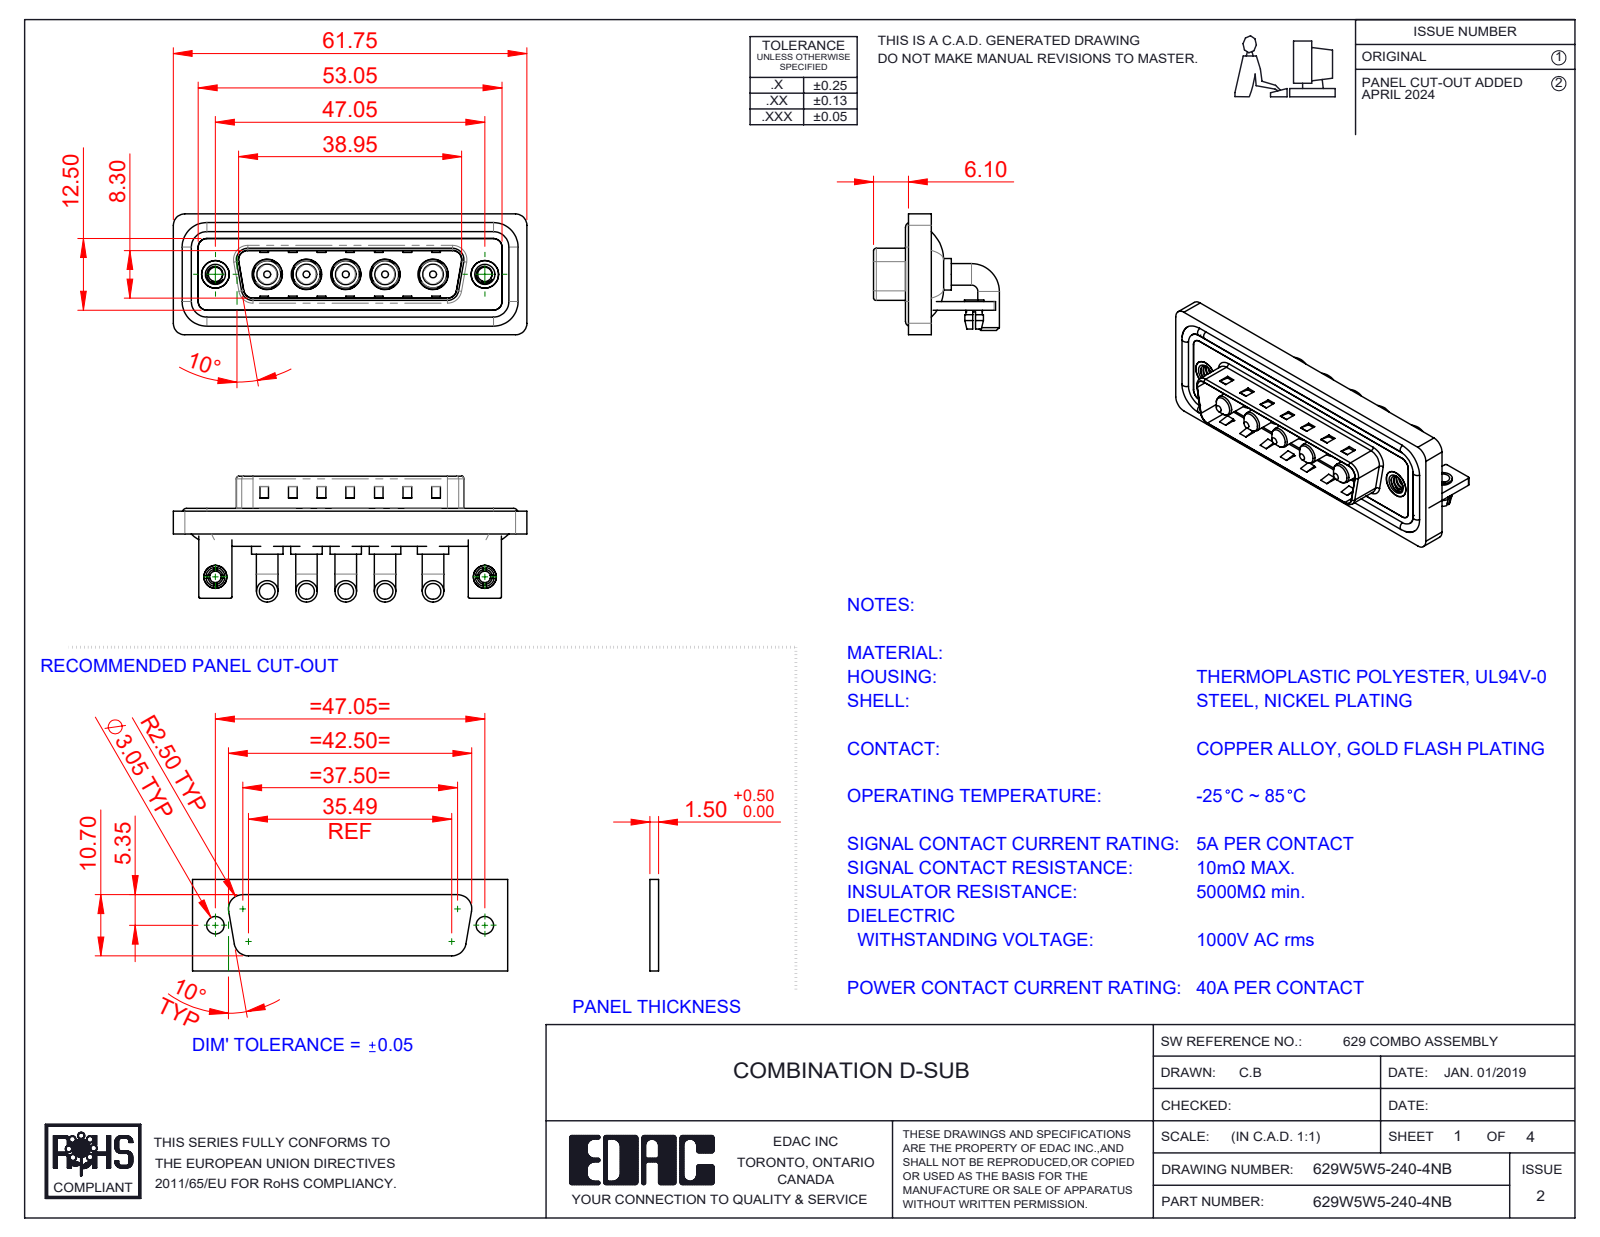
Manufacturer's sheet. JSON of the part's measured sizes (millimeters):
{"part_name": "629Combo Shell Front_25 Contacts; 629Combo Stabilizer Bracket; 629Combo Shell Rear_25 Contacts; 629Combo Housing_5W5 (+5 more)", "step_written_by": "SolidWorks 2023 (CONFIG_CONTROL_DESIGN)", "units": "millimeters", "bodies": {"solids": 21, "faces": 828, "planar": 327, "cylindrical": 343, "other": 158}, "overall_size": [61.75, 21.98, 21.1], "volume_mm3": 8475, "surface_area_mm2": 13290, "round_holes": [[4.85, 5], [5.3, 5], [2.5, 4], [2, 2], [3.2, 2], [4, 2], [4.8, 2], [5, 2]], "round_bosses_or_shafts": [[3.75, 10], [5.5, 5], [5.2, 5], [4.75, 5], [3.6, 5], [1.6, 4], [4.9, 2], [4, 2]], "partial_cylinders_radius": [[2, 19], [1.5, 18], [0.25, 16], [0.5, 9], [1.6, 8], [2.1, 5], [0.6, 4], [0.65, 4]], "face_to_face_distances": [0.4, 1.5, 2.9, 0.8, 2.1, 3.7, 1.1, 4.5, 4.1, 1.2], "hole_center_spacings": [6.86, 13.73, 47.05, 6.85, 6.87, 8.37, 8.38, 9.04]}
